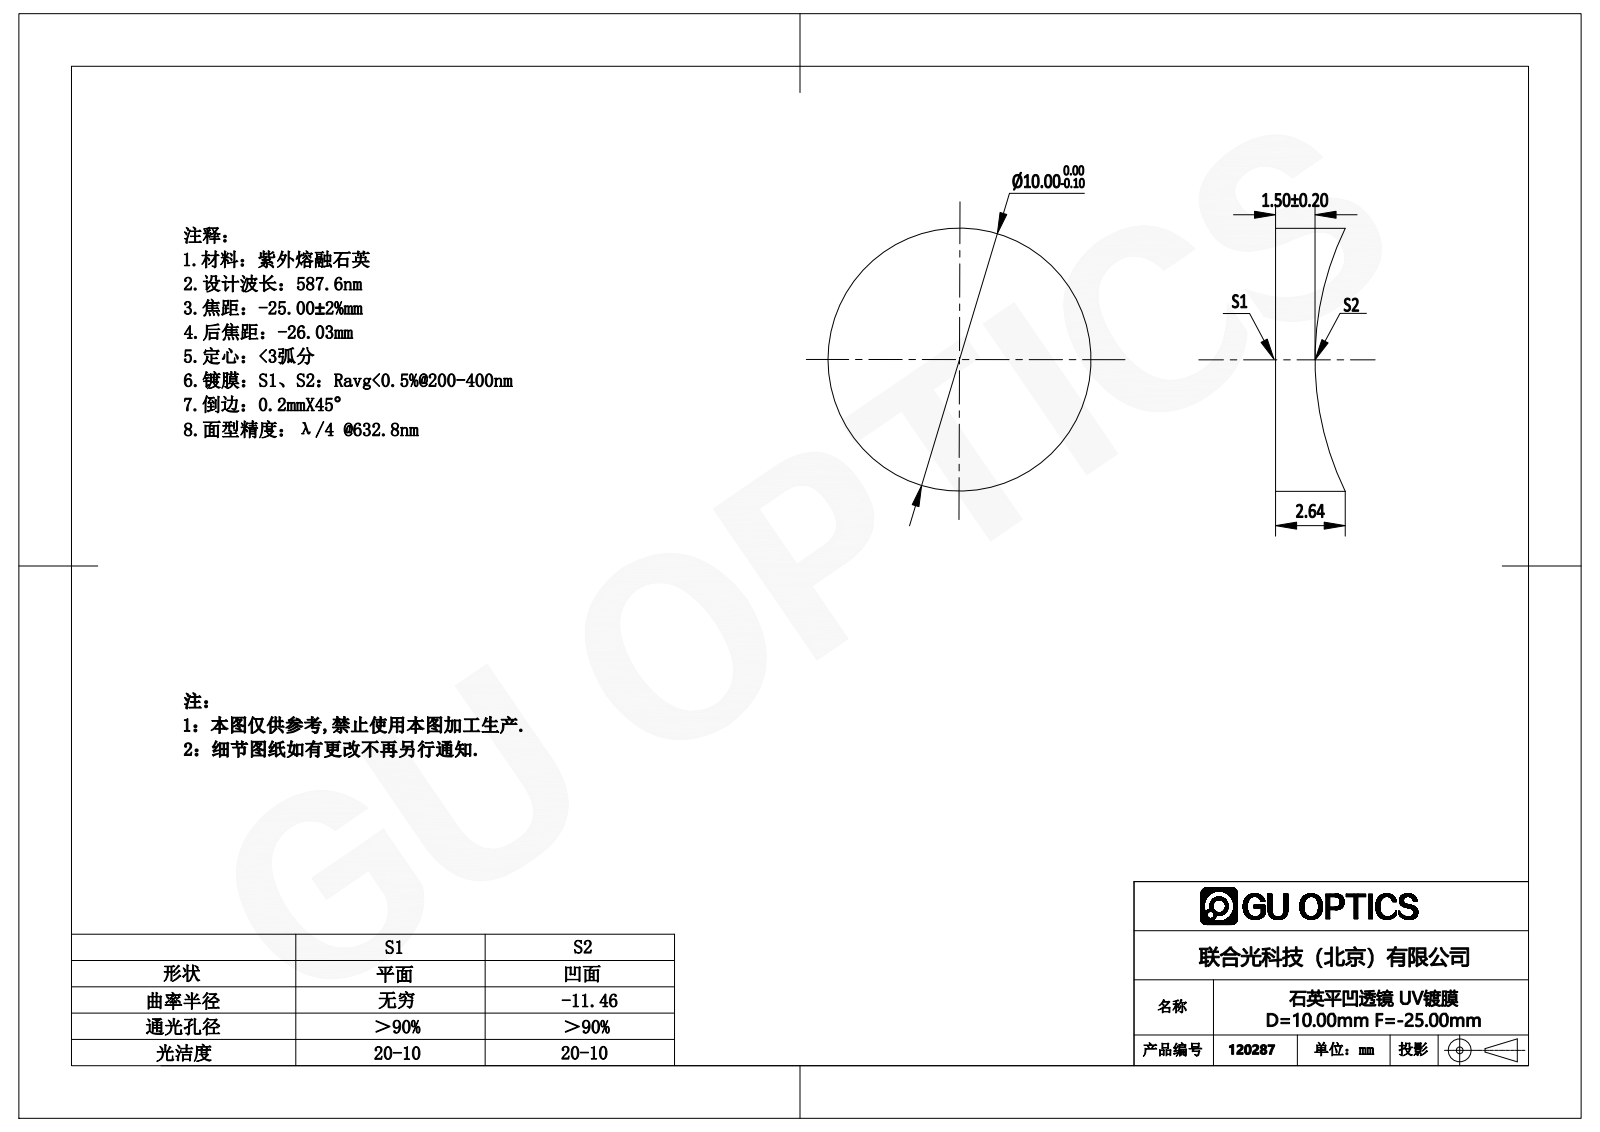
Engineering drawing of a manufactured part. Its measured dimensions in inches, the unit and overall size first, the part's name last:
Units: inches
Overall size (bounding box): 0.394 × 0.394 × 0.104
Round bosses / shafts (diameter × count): ⌀0.394 ×1
Volume: 0.01 in³ · Surface area: 0.378 in²
Bodies: 1 solid, 5 faces (1 planar, 2 cylindrical, 2 other)
Part name (STEP PRODUCT): 120254
STEP written by: SolidWorks 2016 (AUTOMOTIVE_DESIGN)
